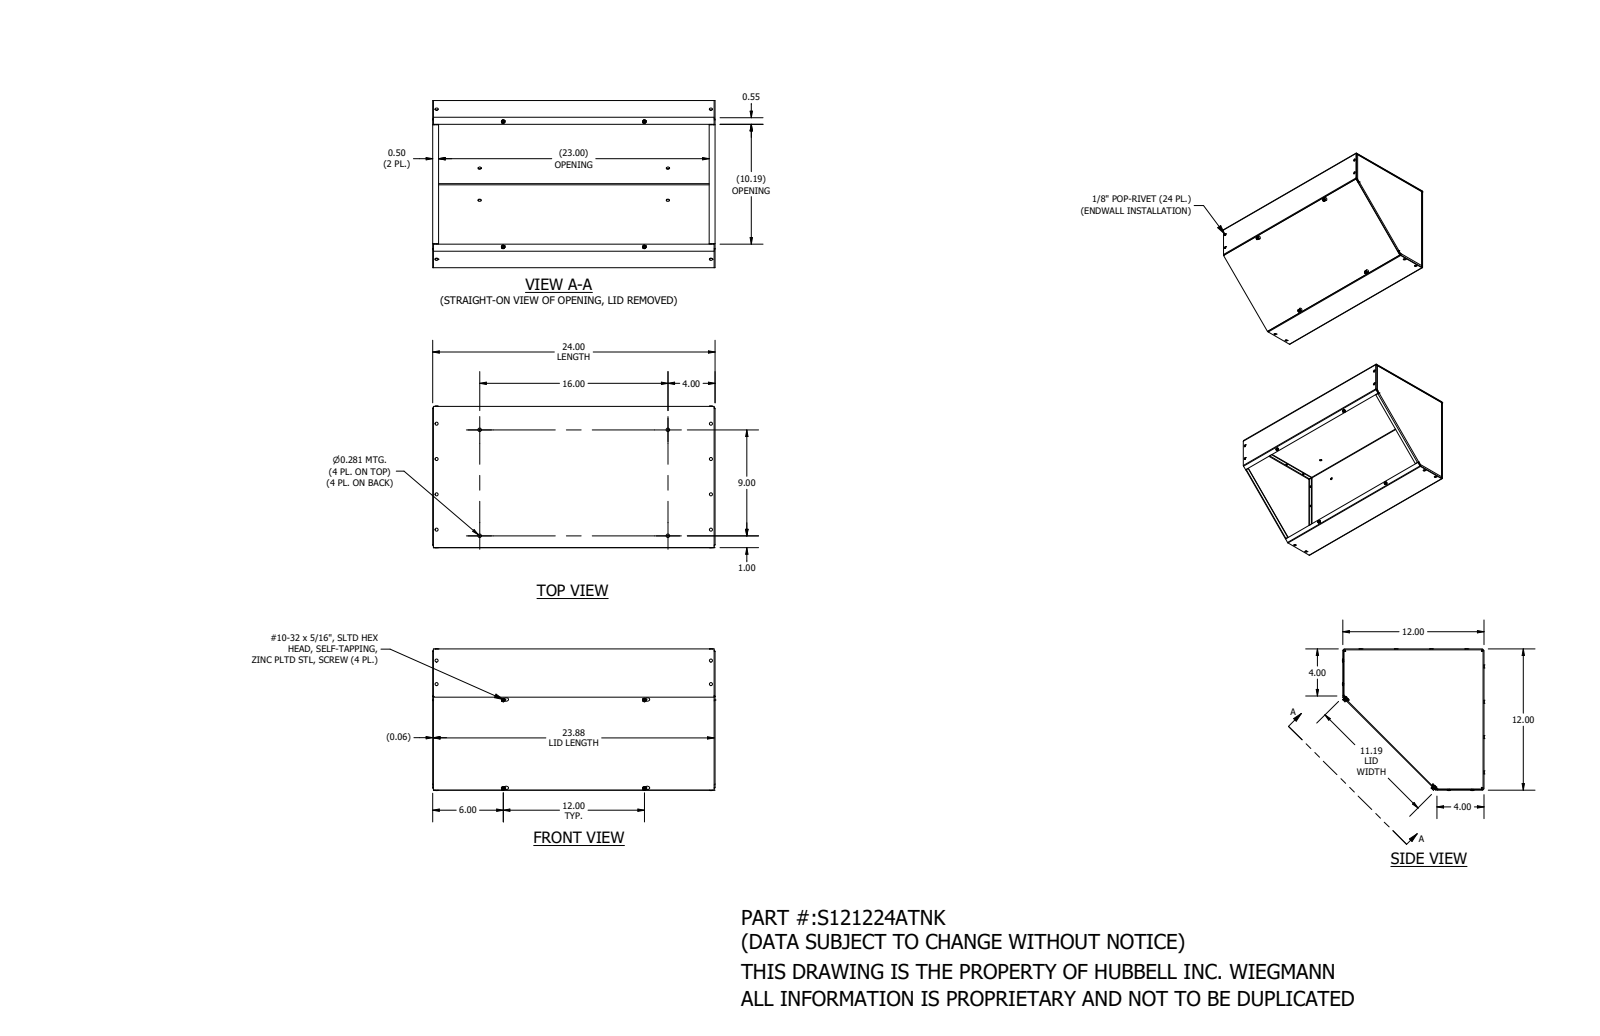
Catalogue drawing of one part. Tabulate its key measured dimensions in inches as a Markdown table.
| quantity | value |
| --- | --- |
| part name | S121224ATNK |
| STEP written by | SolidWorks 2021 (AUTOMOTIVE_DESIGN) |
| units | inches |
| bodies | 32 solids, 1210 faces (308 planar, 382 cylindrical, 520 other) |
| overall size | 24 × 12.08 × 12.08 |
| volume | 96.06 in³ |
| surface area | 2 623 in² |
| round holes (diameter × count) | 0.129 × 24, 0.281 × 8, 0.171 × 4, 0.406 × 4 |
| round bosses / shafts (diameter × count) | 0.262 × 24, 0.125 × 18, 0.125 × 6, 0.313 × 4, 0.181 × 4 |
| partial cylindrical surfaces (radius × count) | 0.064 × 48, 0.136 × 15, 0.063 × 11, 0.062 × 4, 0.109 × 4 |
| main face-to-face distances | 0.074, 11.926, 23.926, 11.852, 12, 24, 23.852, 0.067, 0.148, 0.141 |
| hole center spacings | 3, 23.313, 23.505, 1.5, 3.693, 6, 9, 19.663 |
